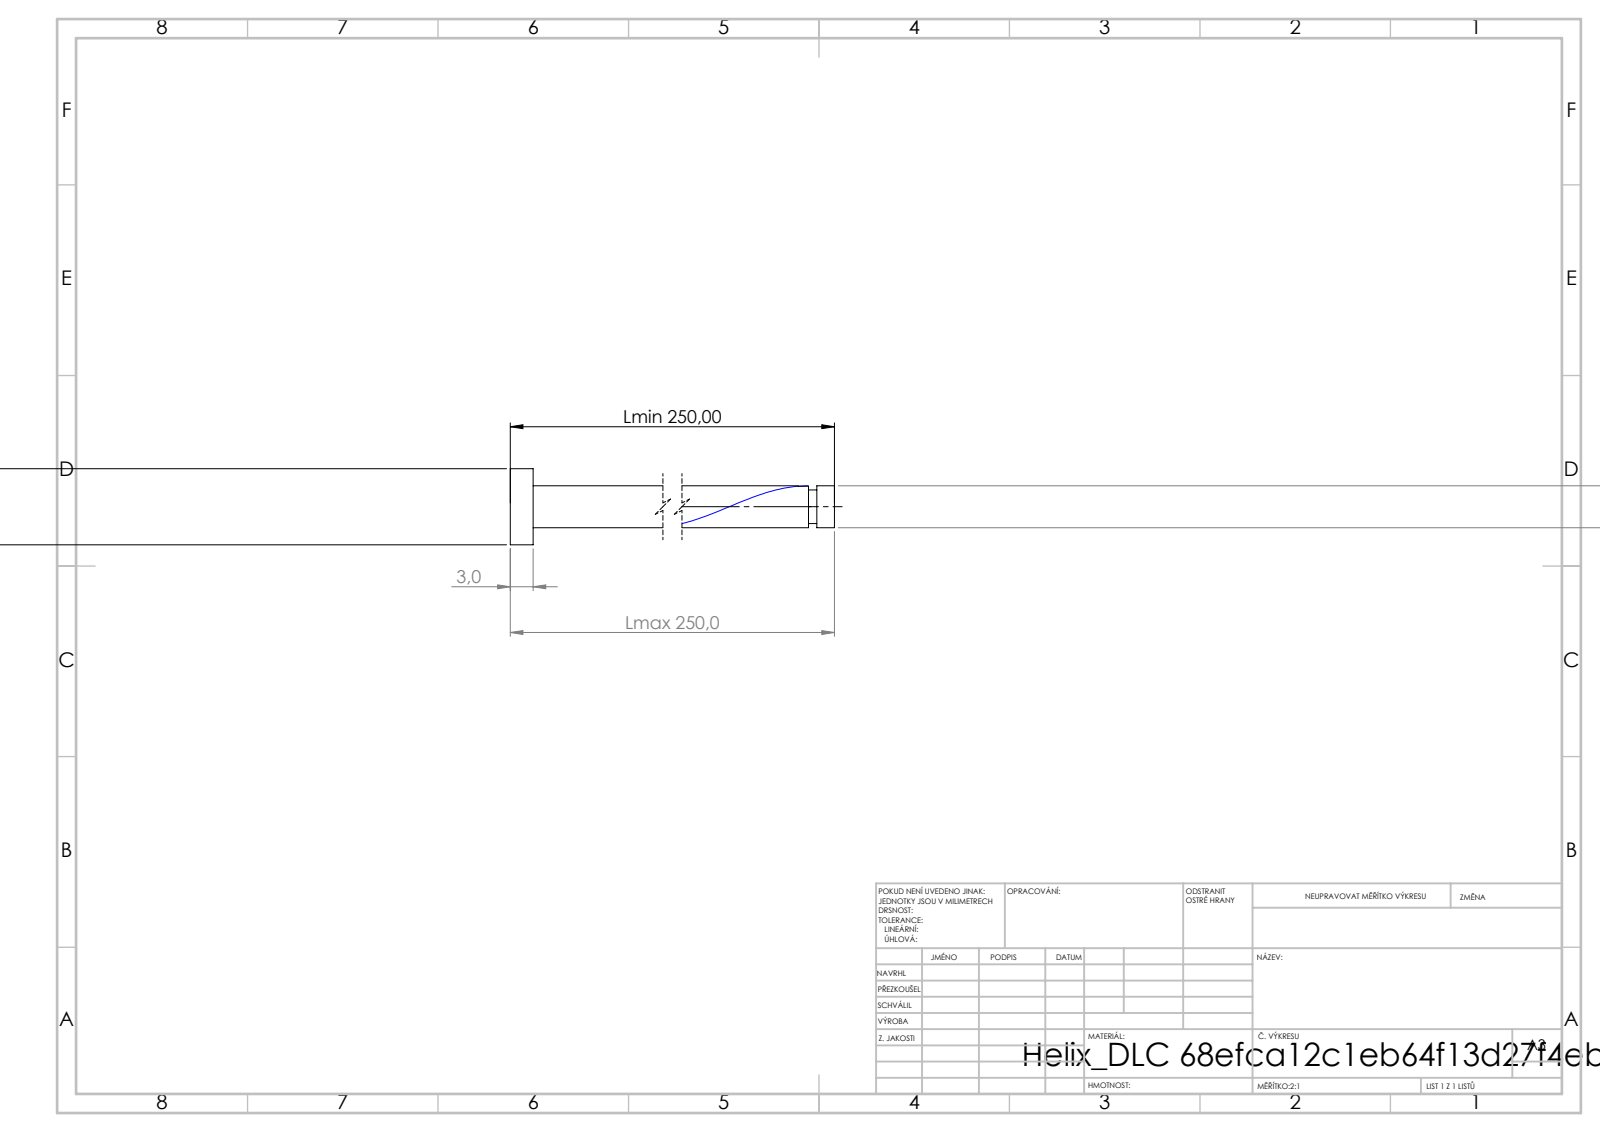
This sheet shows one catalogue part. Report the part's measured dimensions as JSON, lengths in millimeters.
{"step_written_by": "SolidWorks 2019 (CONFIG_CONTROL_DESIGN)", "units": "millimeters", "bodies": {"solids": 1, "faces": 21, "planar": 6, "cylindrical": 14, "other": 1}, "overall_size": [250, 10, 10], "volume_mm3": 6038, "surface_area_mm2": 4605, "round_bosses_or_shafts": [[10, 1], [5.5, 1], [4.4, 1]], "face_to_face_distances": [3, 250, 247, 247.7, 244.7, 2.3, 246.6, 243.6, 1.1, 3.4]}
